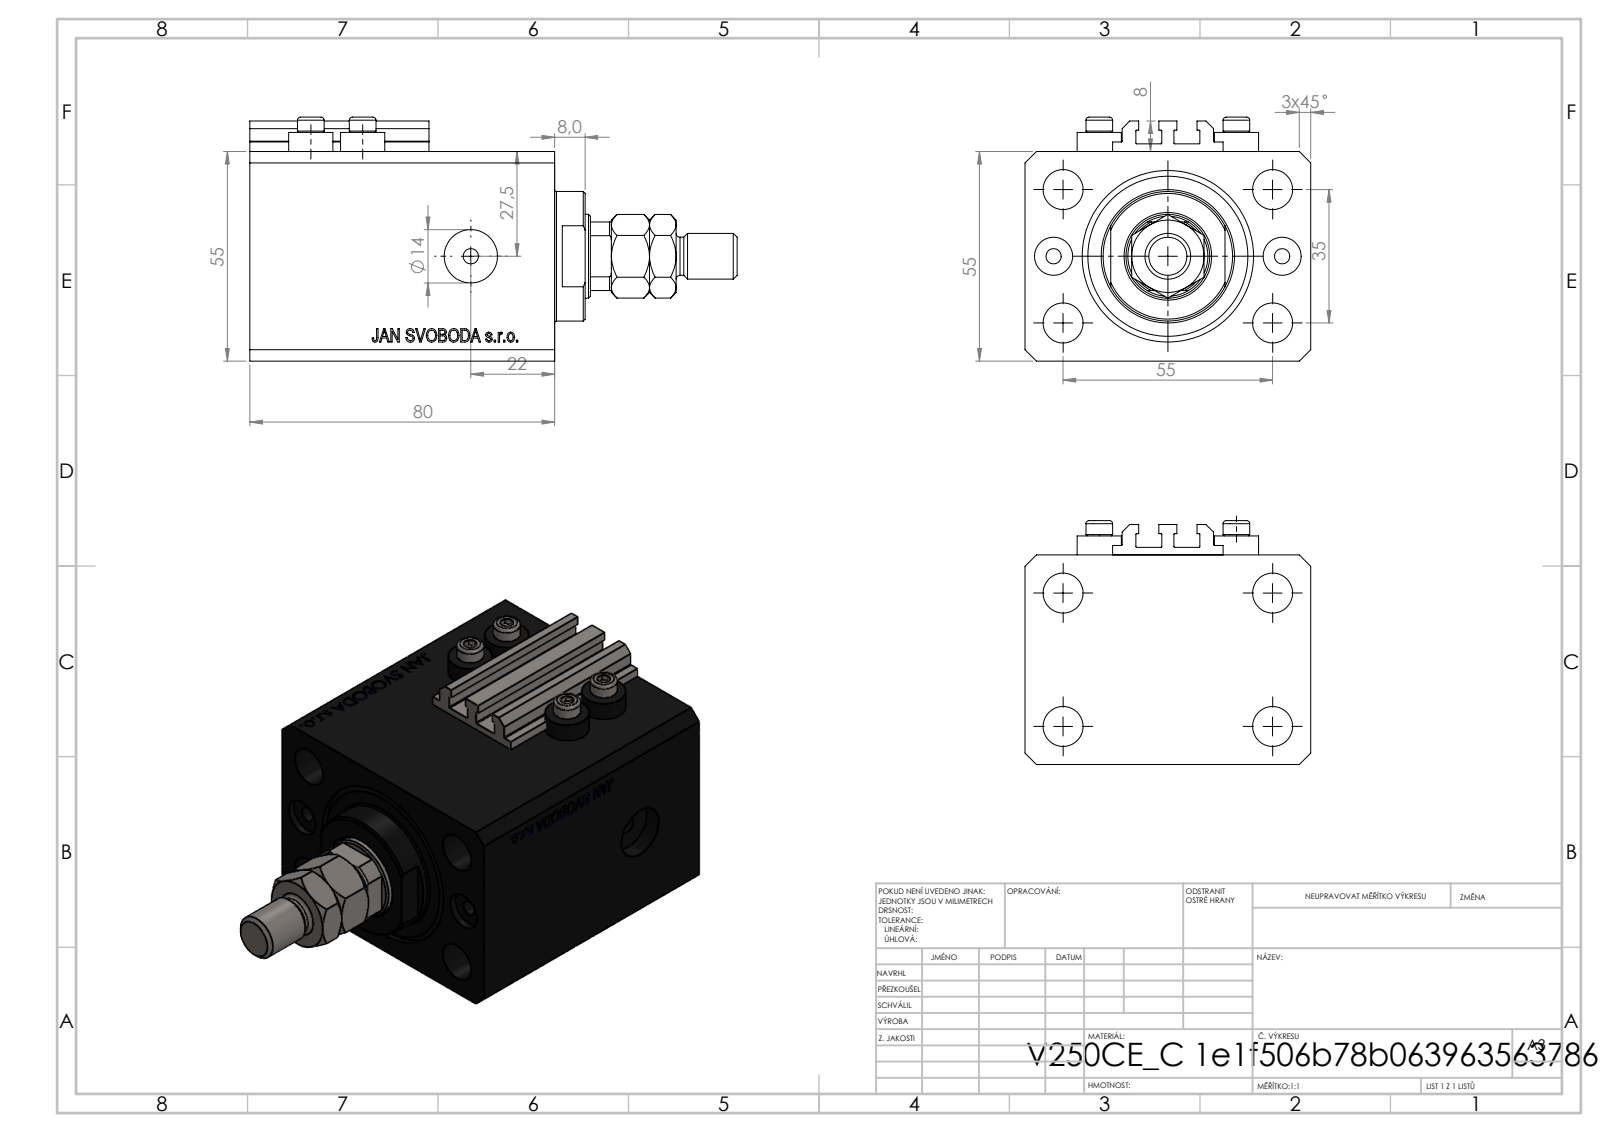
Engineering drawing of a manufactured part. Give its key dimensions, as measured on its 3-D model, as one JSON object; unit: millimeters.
{"part_name": "V250CE_VC_C; MTA; V250CE_C_Body; V250CE_C_VCP (+1 more)", "step_written_by": "SolidWorks 2019 (CONFIG_CONTROL_DESIGN)", "units": "millimeters", "bodies": {"solids": 9, "faces": 1083, "planar": 519, "cylindrical": 90, "other": 474}, "overall_size": [128, 75, 64], "volume_mm3": 312025, "surface_area_mm2": 73774, "round_holes": [[4, 8], [10.5, 5], [10, 2], [14, 2], [22, 1], [32, 1], [45, 1]], "round_bosses_or_shafts": [[11.6, 4], [7, 4], [34, 1], [12, 1], [10, 1]], "partial_cylinders_radius": [[0.2, 10], [10.5, 1]], "face_to_face_distances": [55, 75, 15, 80, 65, 9.9, 55.1, 70.1, 3, 2.5], "hole_center_spacings": [17.68, 32.6, 60.1, 36, 13.6, 30, 35, 38.48]}
